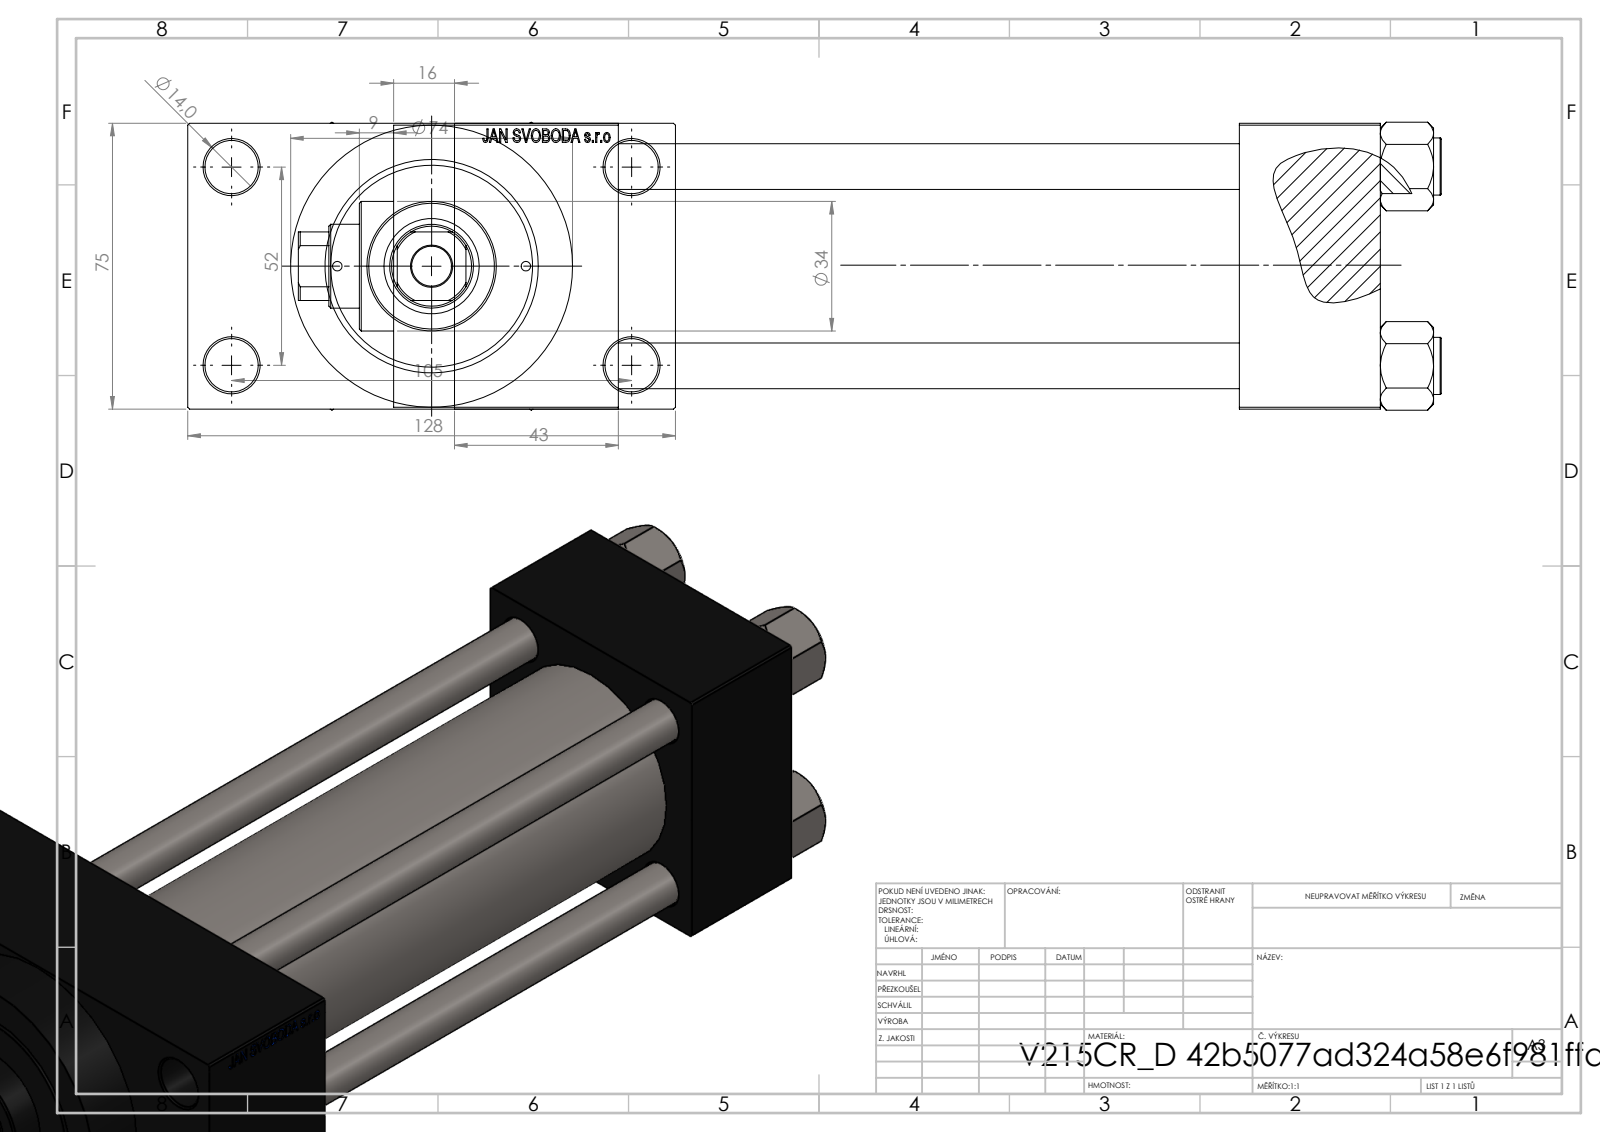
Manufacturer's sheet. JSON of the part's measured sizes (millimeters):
{"part_name": "V215CR_D_Body; V215CR_VCP_D; V215_VC_A; V215CR_D_TYCINKA (+1 more)", "step_written_by": "SolidWorks 2019 (CONFIG_CONTROL_DESIGN)", "units": "millimeters", "bodies": {"solids": 11, "faces": 1111, "planar": 499, "cylindrical": 92, "other": 520}, "overall_size": [300, 128, 75.54], "volume_mm3": 937142, "surface_area_mm2": 224679, "round_holes": [[12, 4], [14, 4], [2.5, 2], [7, 2], [20.96, 2], [30, 2], [10.5, 1], [22, 1], [25, 1], [41, 1], [50, 1], [53, 1]], "round_bosses_or_shafts": [[15, 4], [74, 1], [56, 1], [34, 1]], "partial_cylinders_radius": [[10.5, 1]], "face_to_face_distances": [75, 163, 37, 200, 26.5, 243, 206, 43, 101.5, 16], "hole_center_spacings": [26.19, 26.35, 36.98, 38.03, 52.3, 57.22, 58.43, 58.59]}
